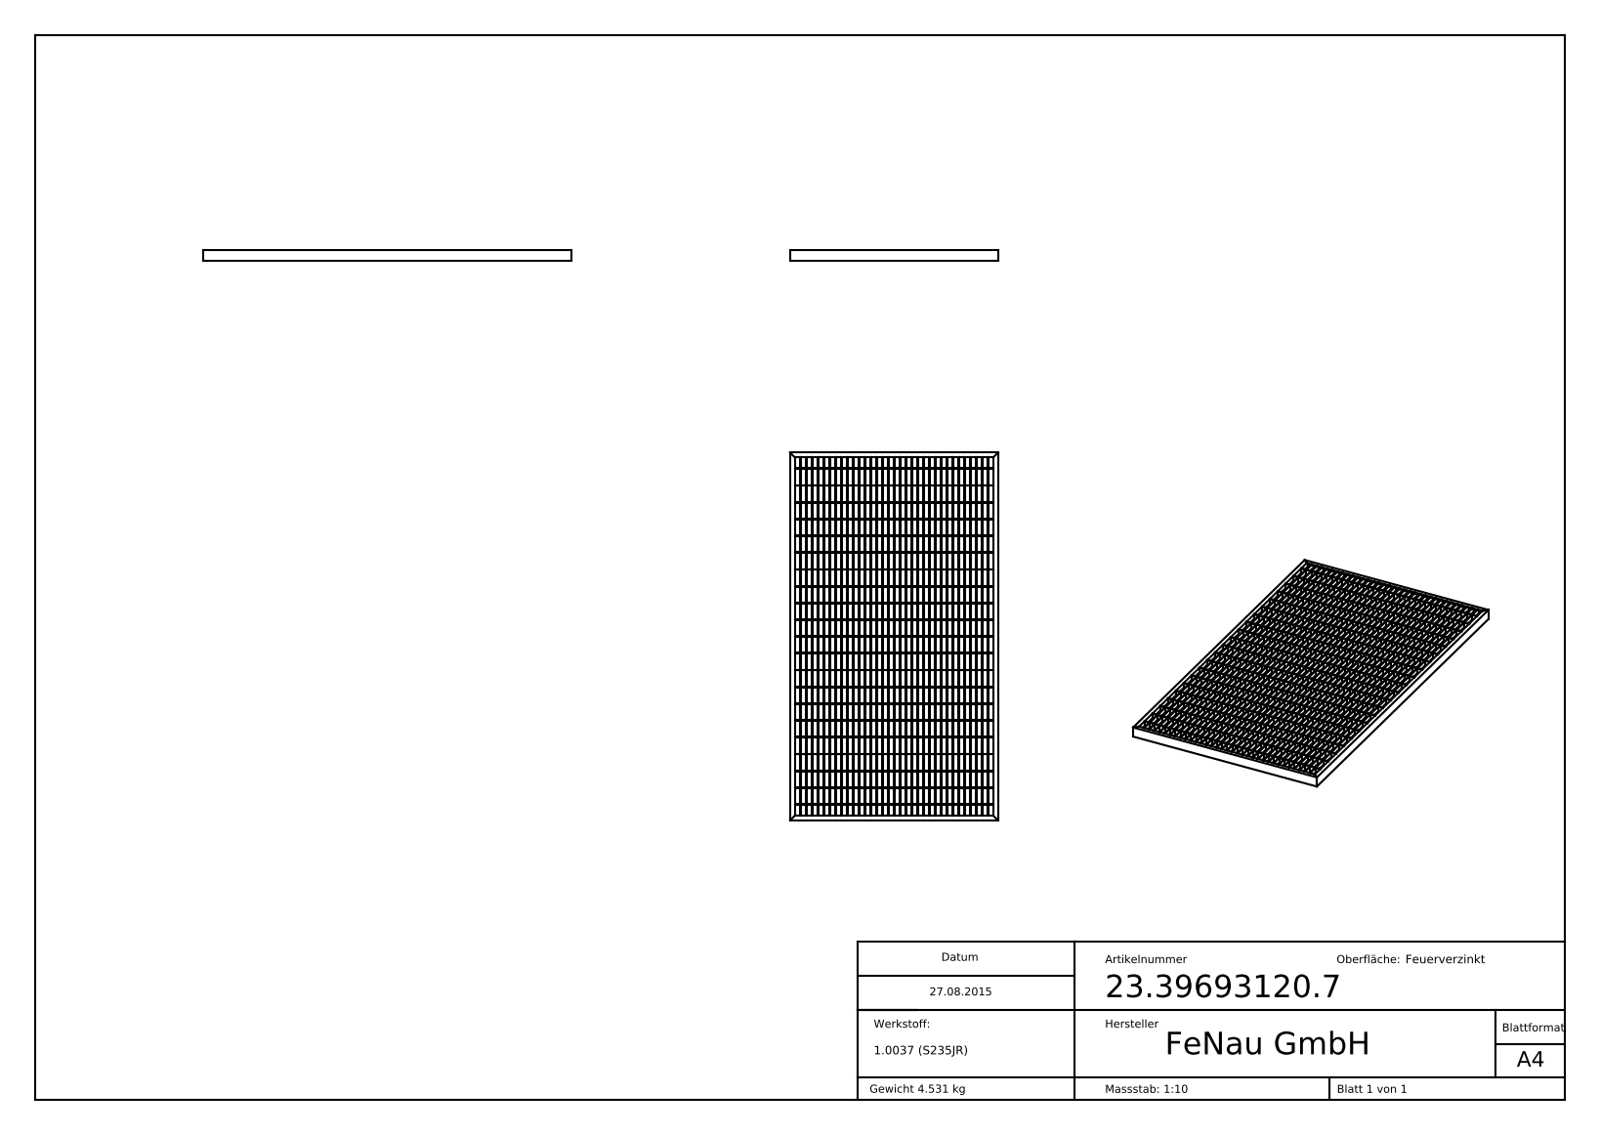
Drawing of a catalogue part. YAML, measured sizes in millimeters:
part_name: "23-39693120-7"
step_written_by: "SolidWorks 2015 (CONFIG_CONTROL_DESIGN)"
units: millimeters
bodies: {solids: 1, faces: 2590, planar: 2590, cylindrical: 0, other: 0}
overall_size: [690, 390, 20]
volume: 580894
surface_area: 945274
face_to_face_distances: [31.5, 63, 94.5, 126, 157.5, 11, 189, 22, 220.5, 33]
